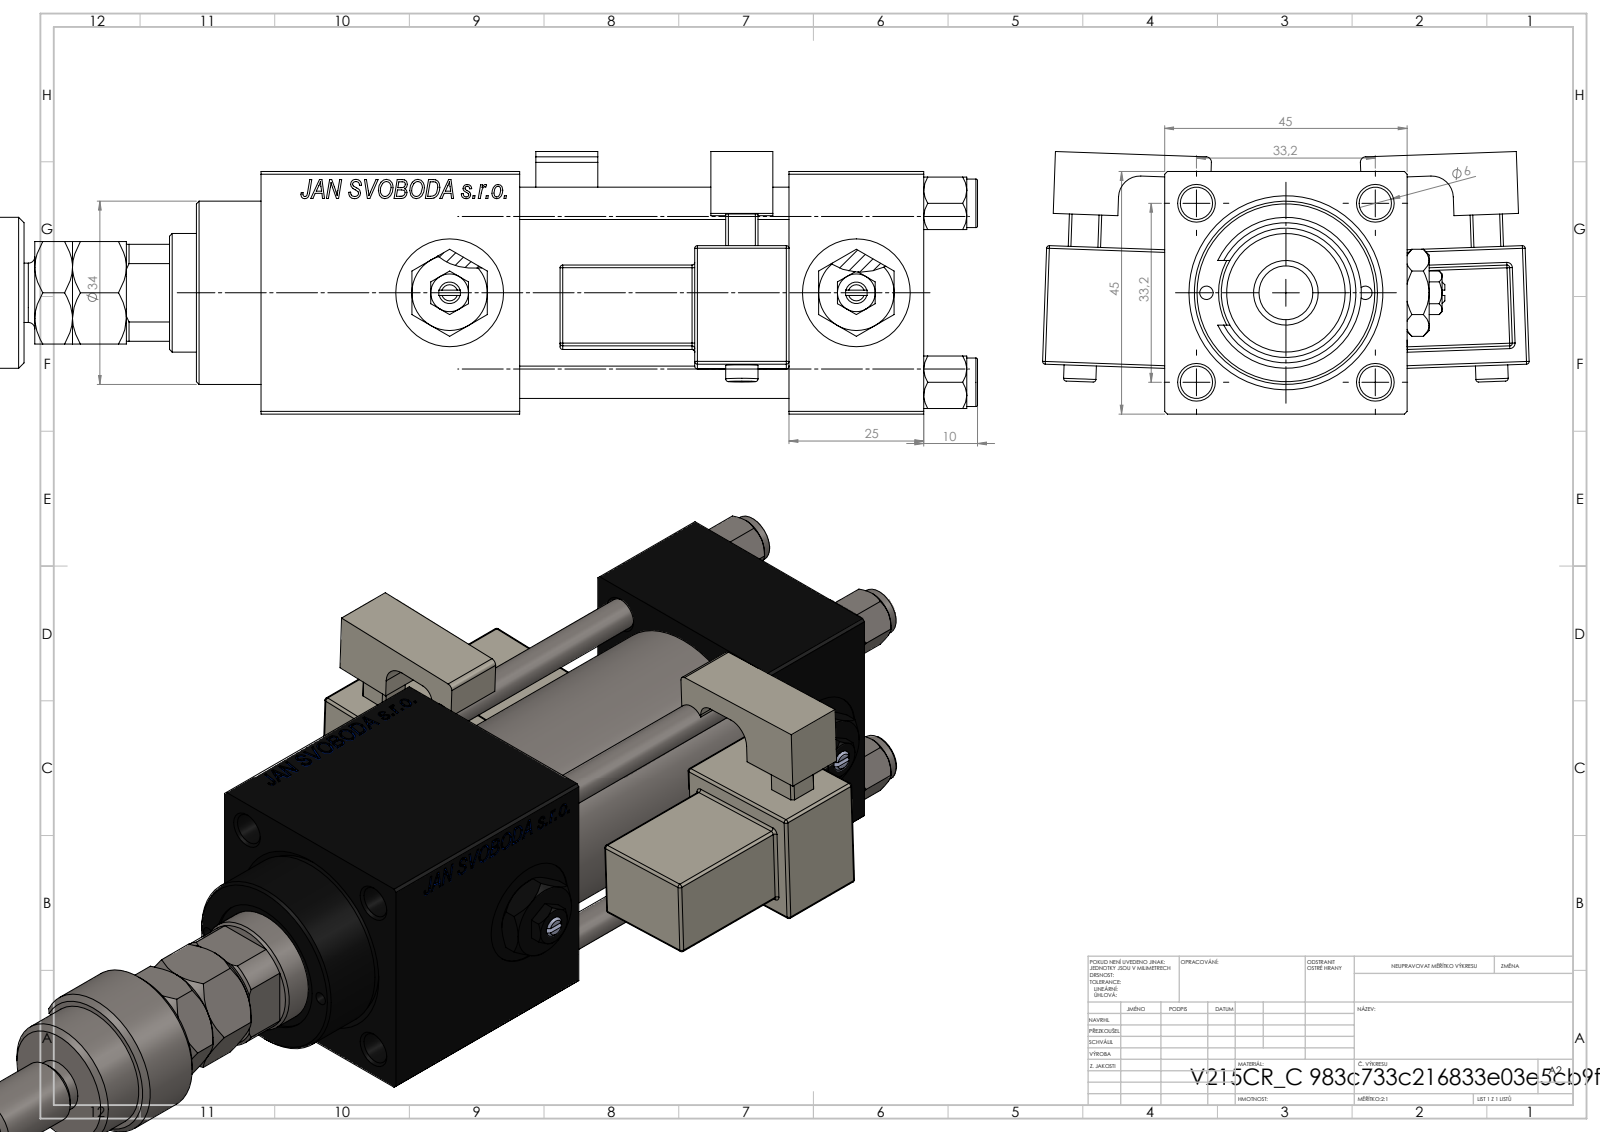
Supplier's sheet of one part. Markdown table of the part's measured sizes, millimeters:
| quantity | value |
| --- | --- |
| part name | V215CR_C_TYCINKA; MFA; V215CR_VCP_C; NUT_M5_C (+5 more) |
| STEP written by | SolidWorks 2019 (CONFIG_CONTROL_DESIGN) |
| units | millimeters |
| bodies | 17 solids, 1497 faces (664 planar, 175 cylindrical, 658 other) |
| overall size | 219 × 90.31 × 48.72 |
| volume | 266 676 mm³ |
| surface area | 92 532 mm² |
| round holes (diameter × count) | 6 × 4, 2.5 × 2, 7 × 2, 13.16 × 2, 20 × 2, 10.5 × 1, 22 × 1, 24 × 1, 25 × 1, 32 × 1, 33 × 1 |
| round bosses / shafts (diameter × count) | 9 × 4, 6 × 2, 38 × 1, 34 × 1, 28 × 1, 18 × 1, 12 × 1, 11 × 1 |
| partial cylindrical surfaces (radius × count) | 0.5 × 48, 1 × 2, 2.5 × 2, 4 × 2, 9.75 × 1, 10.5 × 1 |
| main face-to-face distances | 45, 25, 3, 50, 75, 123, 22.99, 44.8, 14.5, 7.5 |
| hole center spacings | 16.7, 23.48, 33.2, 35.47, 14.75, 46.95, 29.5, 75.5 |
